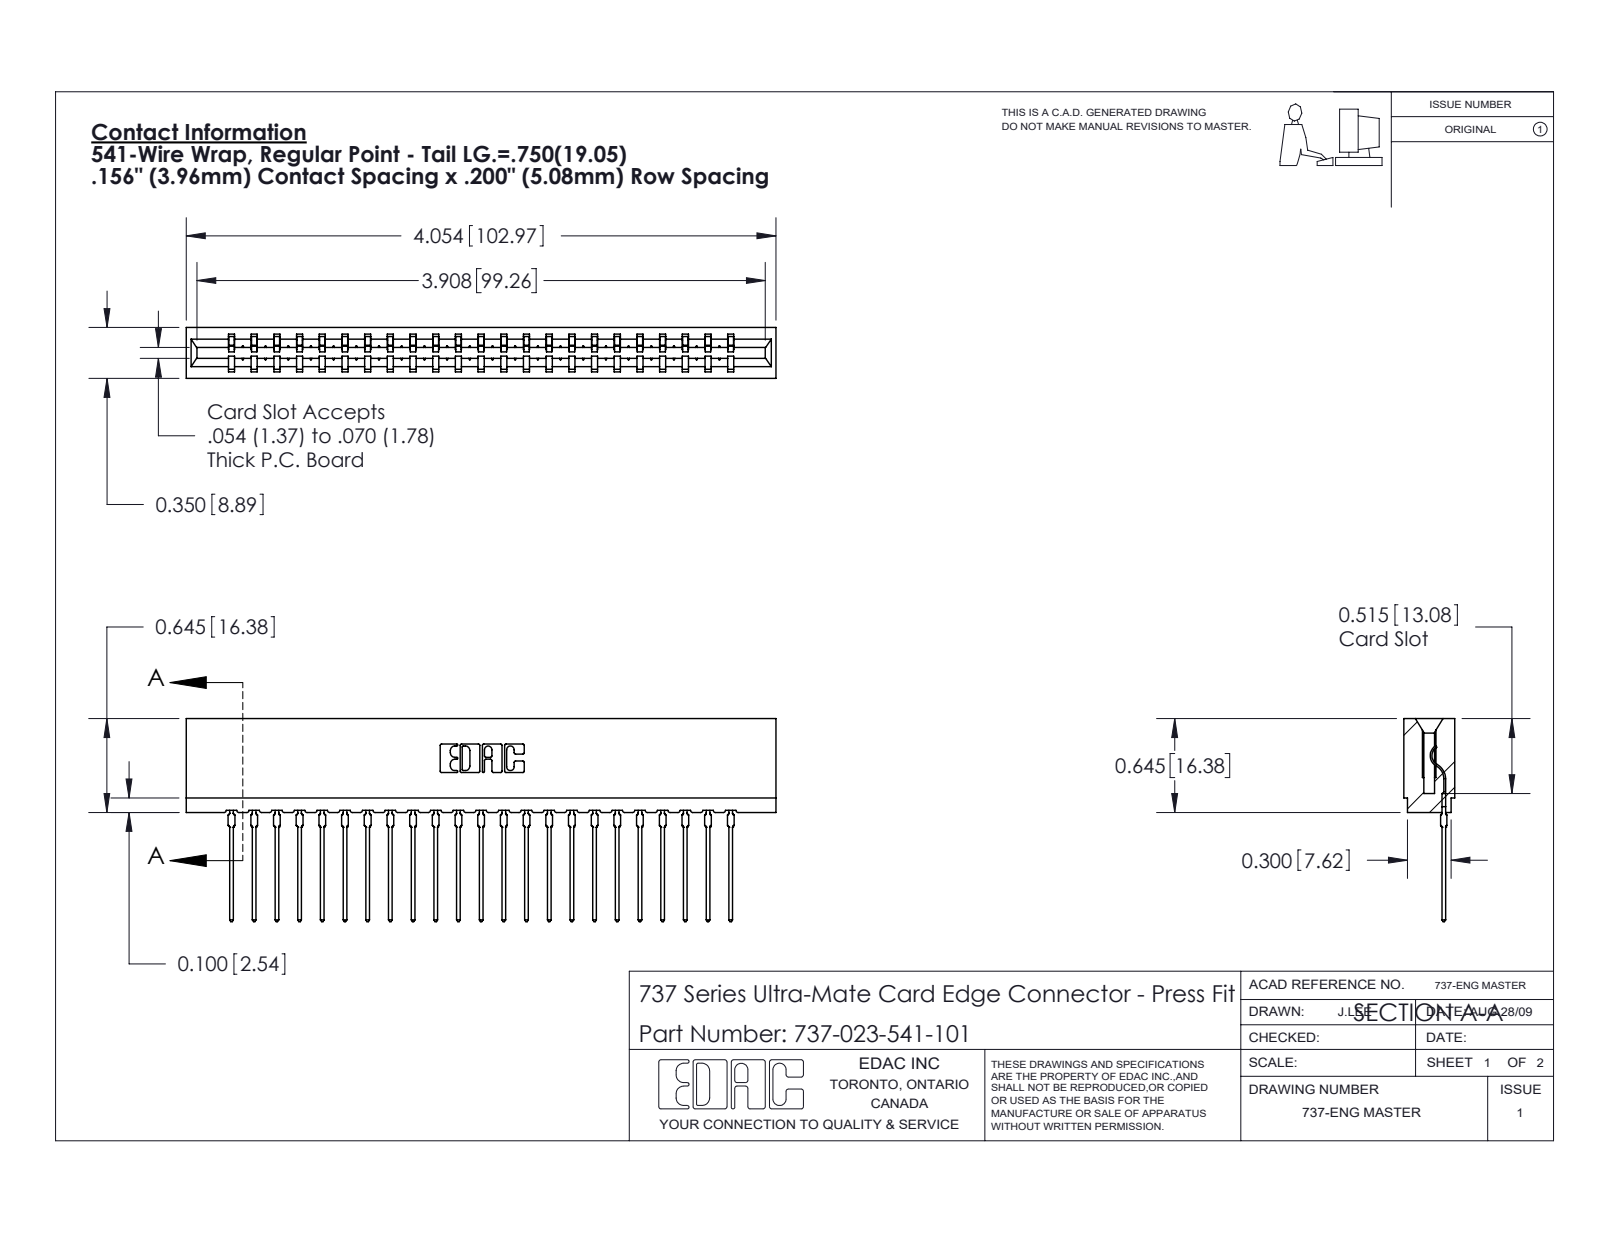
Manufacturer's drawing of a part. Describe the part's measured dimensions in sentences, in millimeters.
The part is named "737 Part_Insulator Option - 01; 745-292-001_541; 737-023-541-101". Its 3-D file was written by "SolidWorks 2020 (CONFIG_CONTROL_DESIGN)". It is 24 solids with 2693 faces: 1618 planar, 477 cylindrical and 598 other. Overall it measures 103 by 35.5 by 8.9 millimeters. Its volume is 10 200 cubic millimeters and its surface area 13 830 square millimeters. Partial cylindrical surfaces (rounded edges, fillets, slot ends): 46 of radius 0.4, 46 of radius 0.5, 22 of radius 0.3, 6 of radius 0.2, 6 of radius 0.8, 4 of radius 0.1, 4 of radius 0.3, 3 of radius 0.7. The main face-to-face distances are 3.5, 5.4, 8.9, 4, 15.8, 1.9, 1.6, 7.3, 1.9, 3.8.
